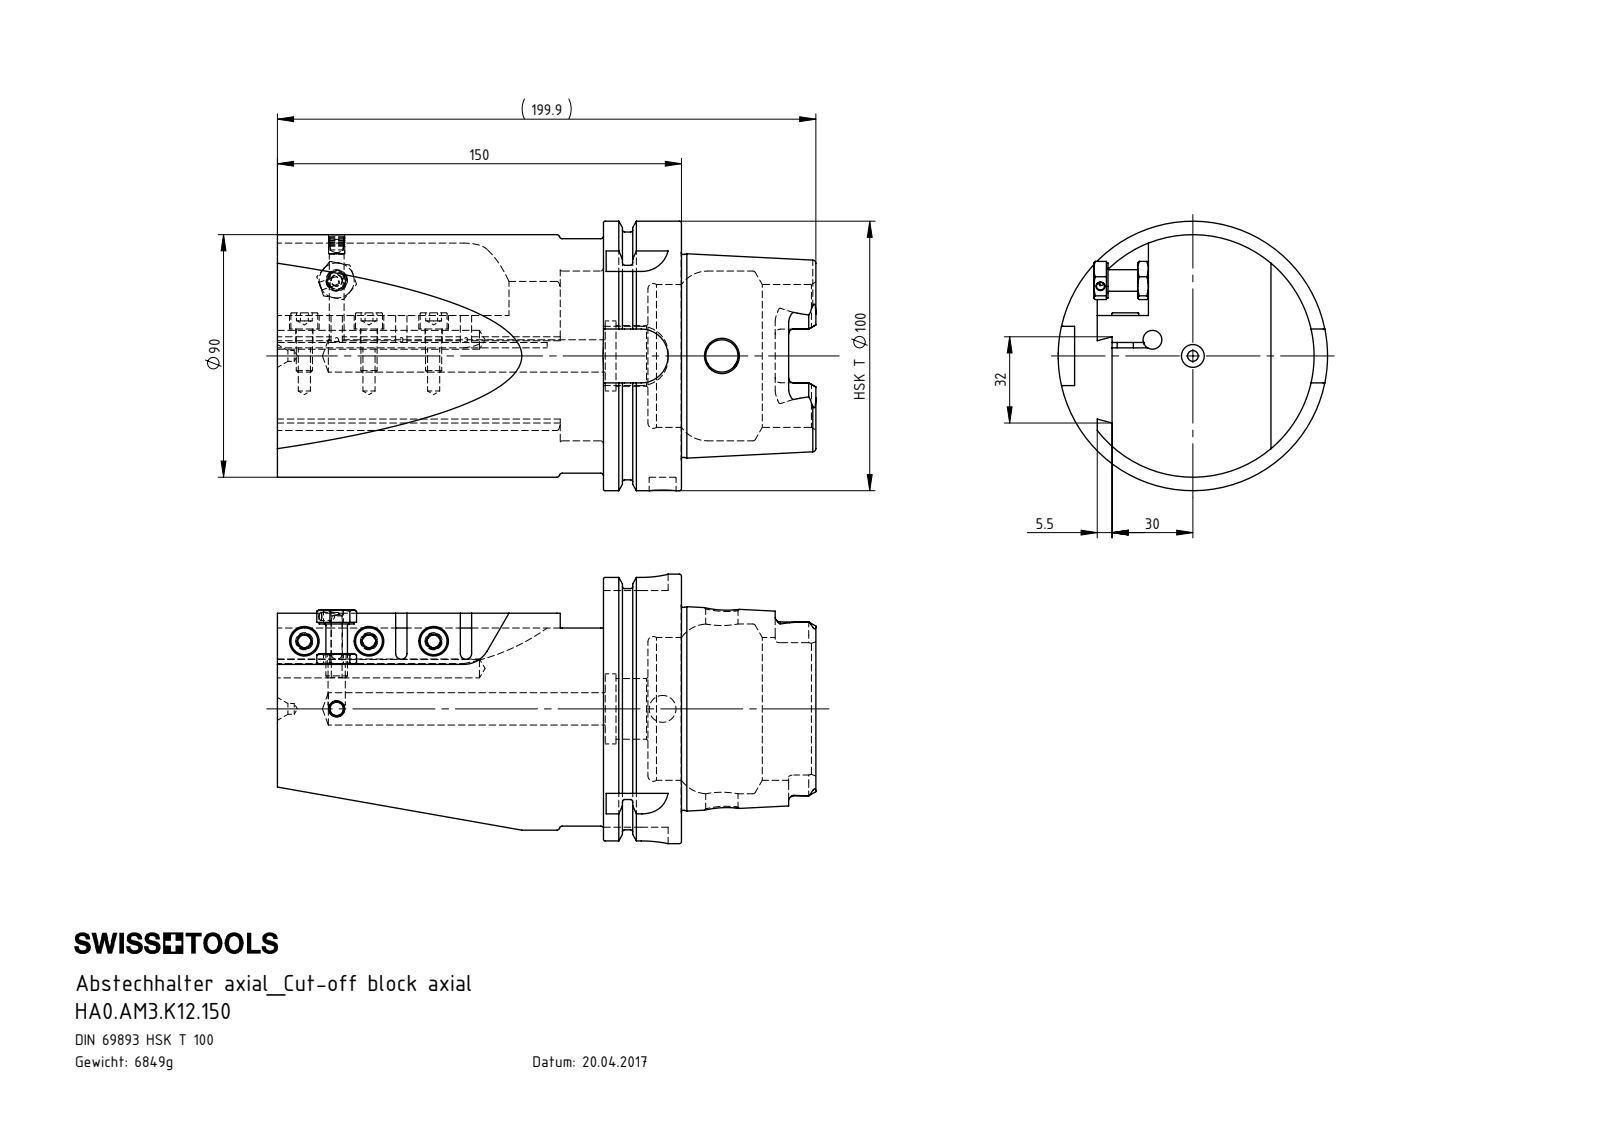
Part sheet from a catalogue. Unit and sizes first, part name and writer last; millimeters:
Units: millimetres
Overall size (bounding box): 199.9 × 100 × 100
Round holes (diameter × count): ⌀6.4 ×4, ⌀4.5 ×3, ⌀11 ×3, ⌀4 ×2, ⌀7 ×2, ⌀12 ×2, ⌀3 ×1, ⌀5 ×1, ⌀5.5 ×1, ⌀10 ×1, ⌀22.5 ×1, ⌀26 ×1
Round bosses / shafts (diameter × count): ⌀6 ×4, ⌀10 ×3, ⌀100 ×1, ⌀91.95 ×1, ⌀75.31 ×1, ⌀13 ×1, ⌀8 ×1
Partial cylindrical surfaces — rounded edges, fillets, slot ends (radius × count): R1.9 ×6, R10 ×5, R2.1 ×3, R4.88 ×2, R4.93 ×2, R43.5 ×1, R45 ×1, R77.5 ×1
Main face-to-face distances: 150, 13.5, 28.95, 121.05, 19, 5.5, 12.45, 16.5, 137.55, 5
Hole centre spacings: 24, 27.82, 16.16, 43.89, 48, 88.63, 111.85, 121
Volume: 873 615 mm³ · Surface area: 99 315 mm²
Bodies: 8 solids, 414 faces (142 planar, 108 cylindrical, 164 other)
Part name (STEP PRODUCT): AM3-ER1.001.020_PreviewCfg; ISO 4035 - M8_PreviewCfg; ISO 4762 - M6 x 16_PreviewCfg; KVT_MB_600_060 (+2 more)
STEP written by: SolidWorks 2015 (AUTOMOTIVE_DESIGN)
